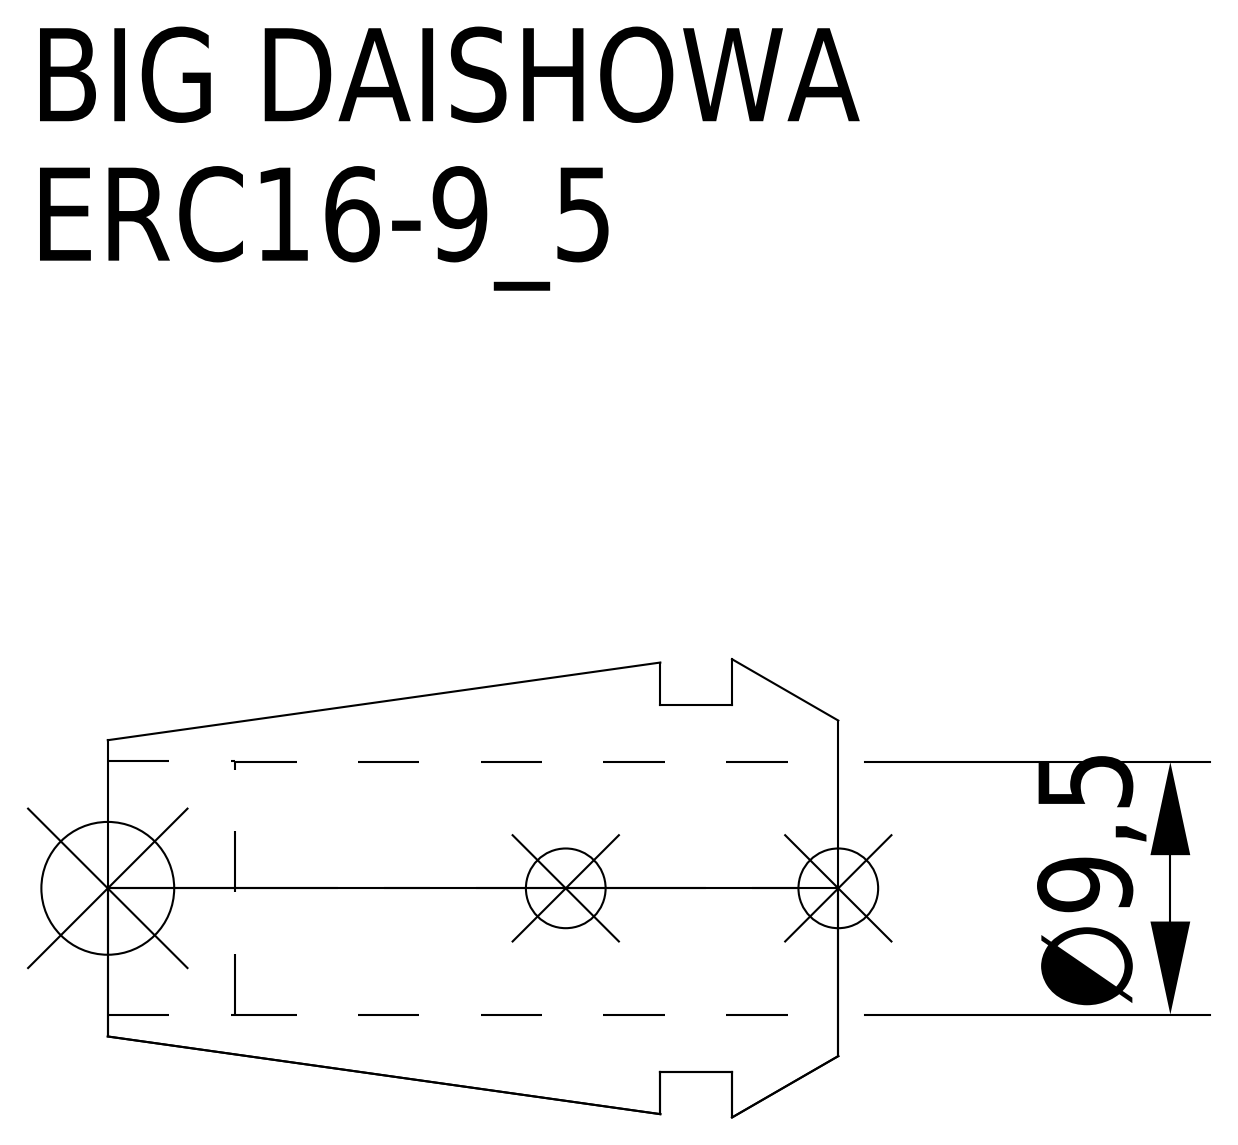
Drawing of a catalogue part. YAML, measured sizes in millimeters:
part_name: "ERC16-9_5"
step_written_by: "CREO PARAMETRIC BY PTC INC, 2016380 (AUTOMOTIVE_DESIGN)"
units: millimeters
bodies: {solids: 1, faces: 15, planar: 5, cylindrical: 6, other: 4}
overall_size: [27.5, 17.25, 17.25]
volume: 2442
surface_area: 2327
round_holes:
  - {diameter: 9.5, count: 1}
  - {diameter: 9.55, count: 1}
round_bosses_or_shafts:
  - {diameter: 13.8, count: 1}
face_to_face_distances: [2.7, 4, 6.7, 27.5, 23.5, 20.8, 22.7, 18.7, 16, 4.8]
